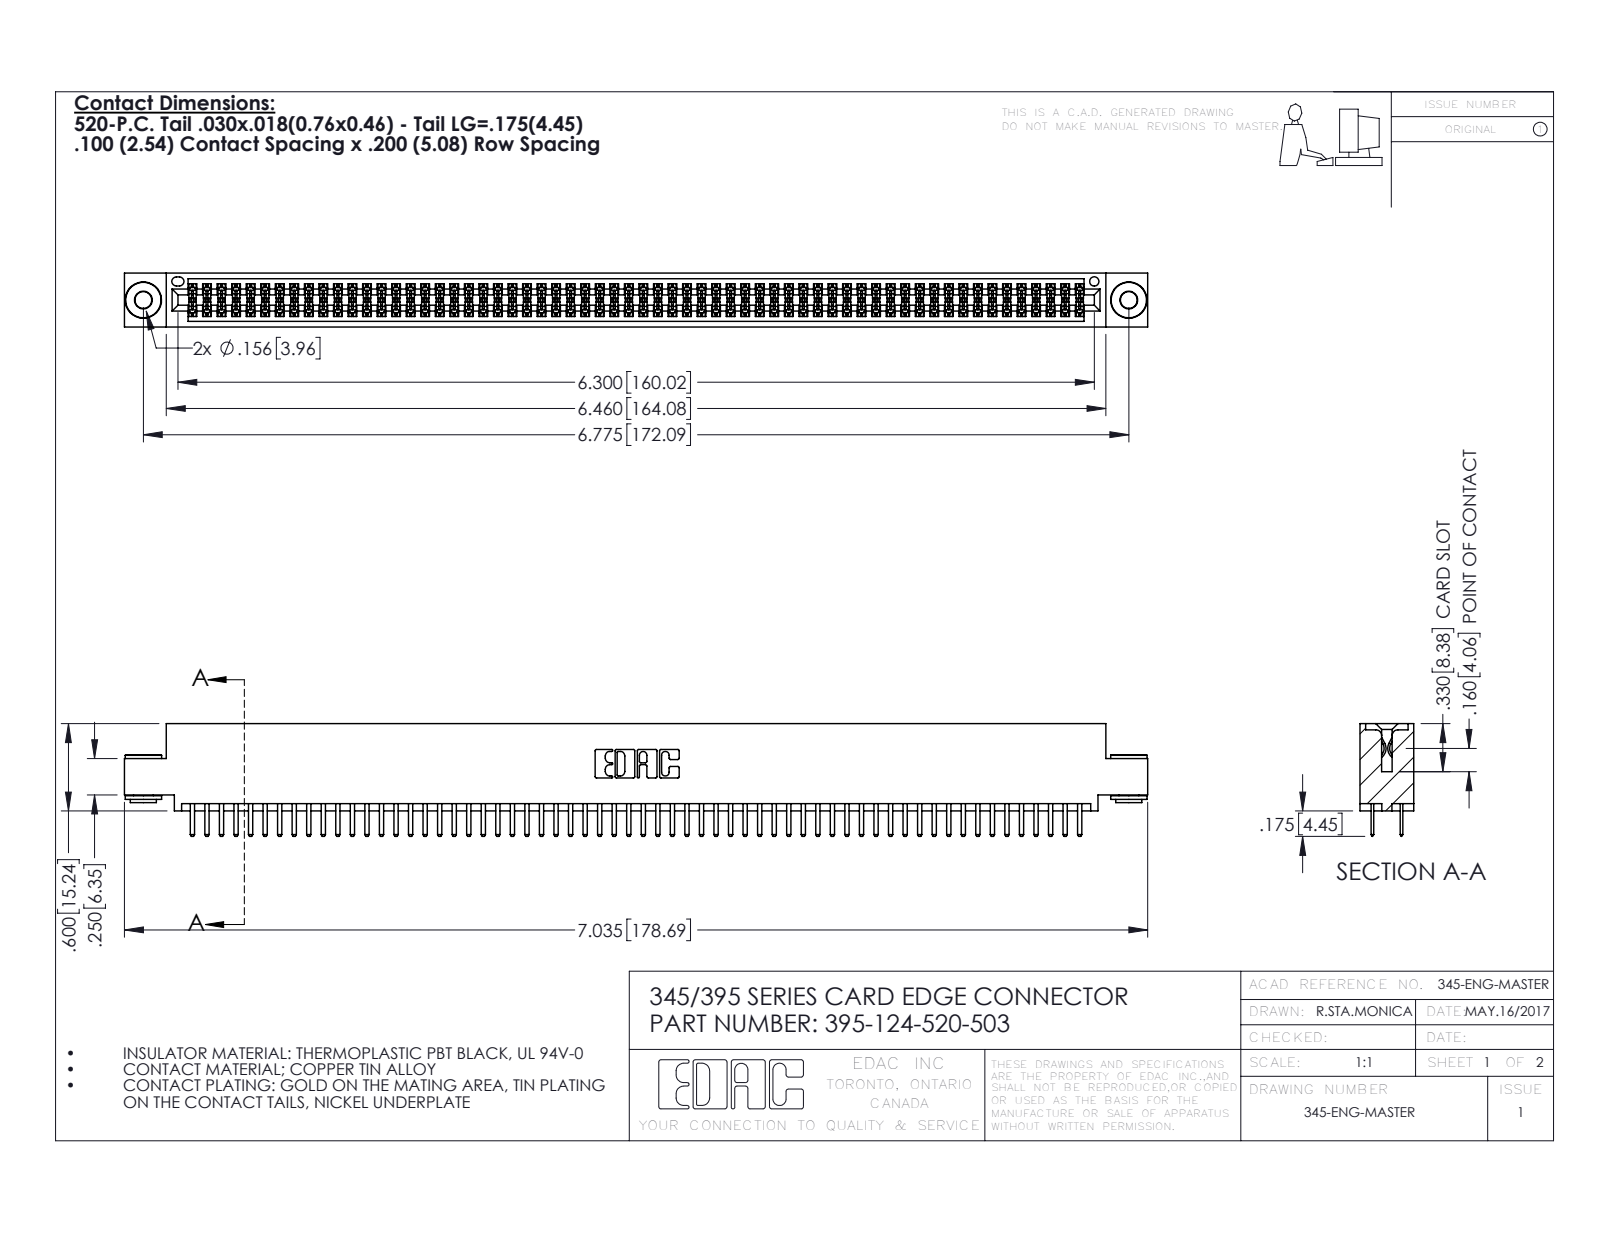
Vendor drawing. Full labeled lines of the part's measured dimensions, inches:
Part name (STEP PRODUCT): 345-292-001_345-293-120; 345-250-002_345-250-002-102; 345 Part_0.110 Offset - 0.156 Dia-TH; 395-124-520-503
STEP written by: SolidWorks 2016 (CONFIG_CONTROL_DESIGN)
Units: inches
Bodies: 127 solids, 6864 faces (4434 planar, 2422 cylindrical, 8 other)
Overall size (bounding box): 7.035 × 0.775 × 0.37
Volume: 1.064 in³ · Surface area: 40.83 in²
Round holes (diameter × count): ⌀0.116 ×2, ⌀0.156 ×2, ⌀0.064 ×1
Round bosses / shafts (diameter × count): ⌀0.25 ×2, ⌀0.18 ×2, ⌀0.136 ×2
Partial cylindrical surfaces — rounded edges, fillets, slot ends (radius × count): R0.006 ×186, R0.01 ×128, R0.01 ×22, R0.007 ×6, R0.031 ×6, R0.026 ×3, R0.014 ×2, R0.019 ×2
Main face-to-face distances: 0.072, 0.298, 0.2, 0.37, 0.025, 0.098, 0.272, 0.225, 0.022, 0.072
Hole centre spacings: 0.27, 6.539, 6.775
